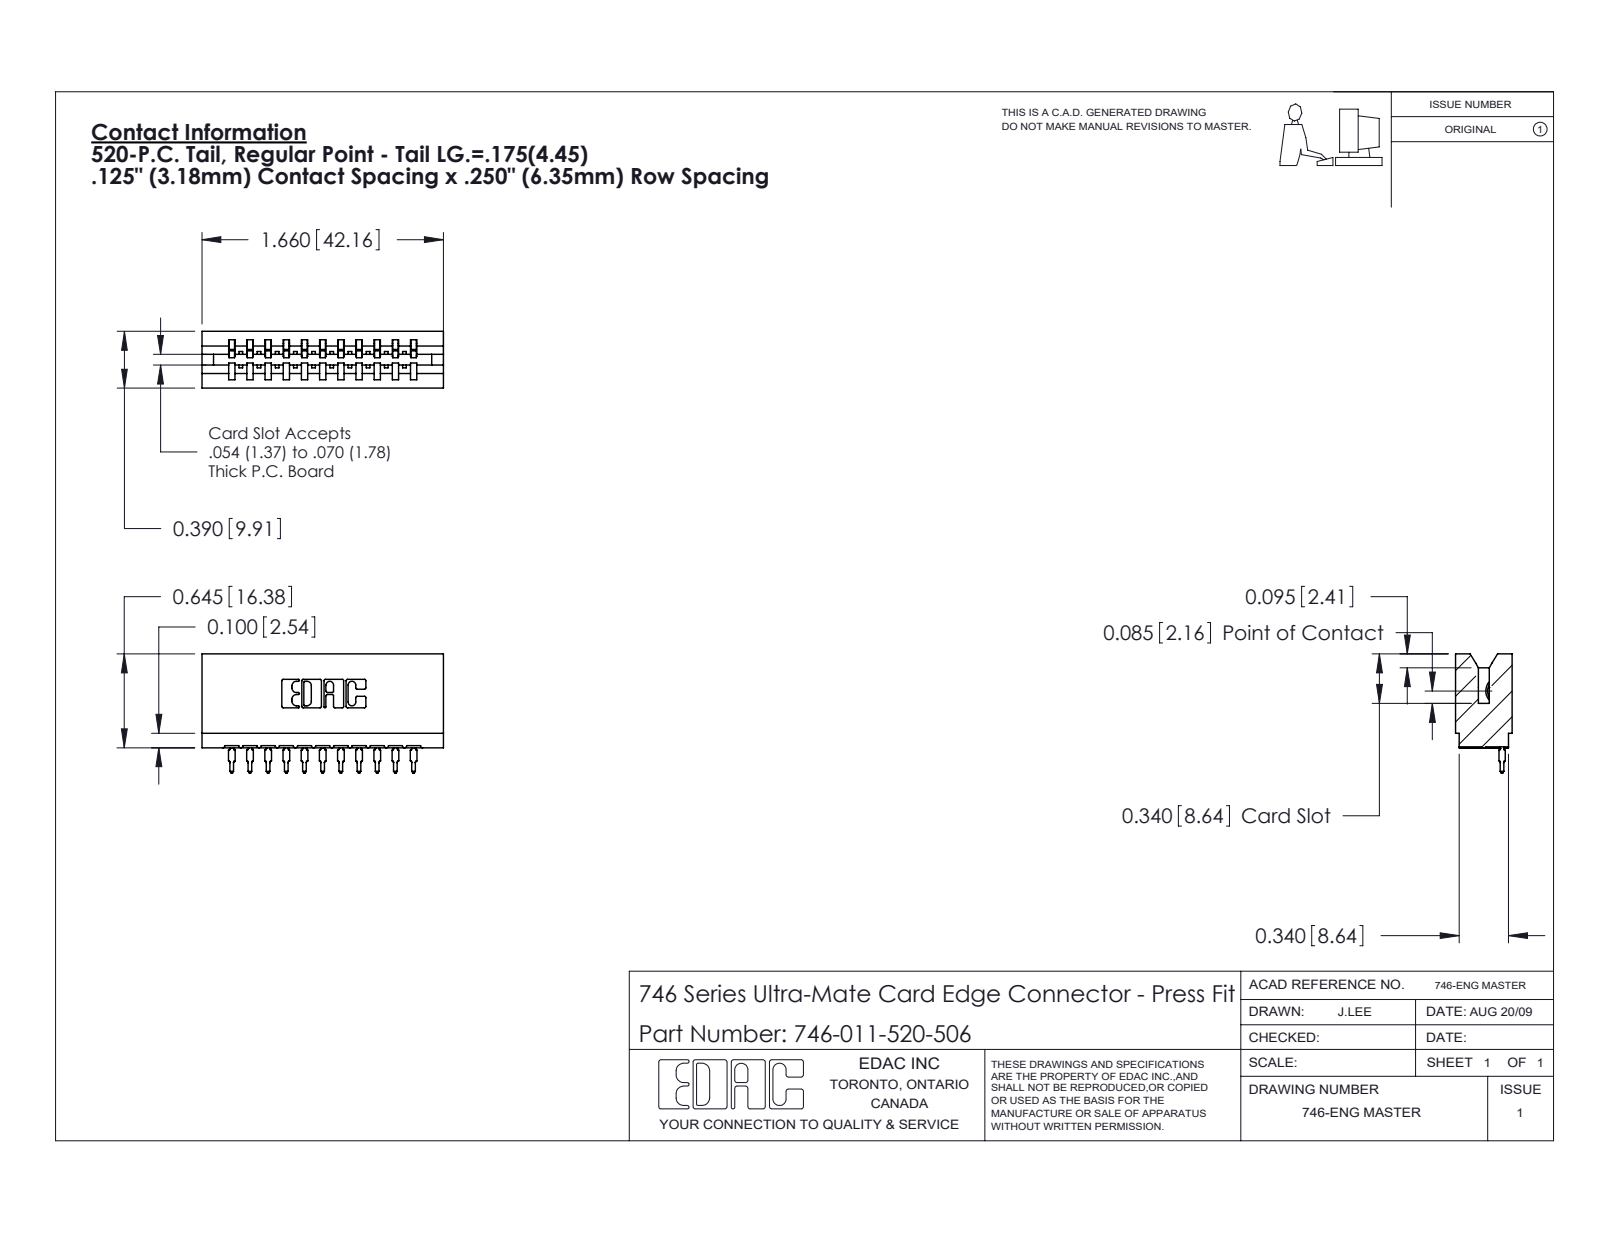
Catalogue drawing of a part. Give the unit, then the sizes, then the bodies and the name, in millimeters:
Units: millimetres
Overall size (bounding box): 42.2 × 20.8 × 9.9
Partial cylindrical surfaces — rounded edges, fillets, slot ends (radius × count): R0.3 ×22, R0.5 ×22, R0.4 ×12, R0.2 ×6, R0.8 ×6, R0.1 ×4, R0.3 ×4, R0.7 ×3
Main face-to-face distances: 6.4, 12.7, 8.5, 3.2, 1.4, 1.1, 3.2, 7.4, 13.8, 9.9
Volume: 4 880 mm³ · Surface area: 6 044 mm²
Bodies: 12 solids, 1286 faces (749 planar, 251 cylindrical, 286 other)
Part name (STEP PRODUCT): 746 Part_.340 Slot Depth - 06; 746-292-001_520; 746-011-520-506
STEP written by: SolidWorks 2020 (CONFIG_CONTROL_DESIGN)
